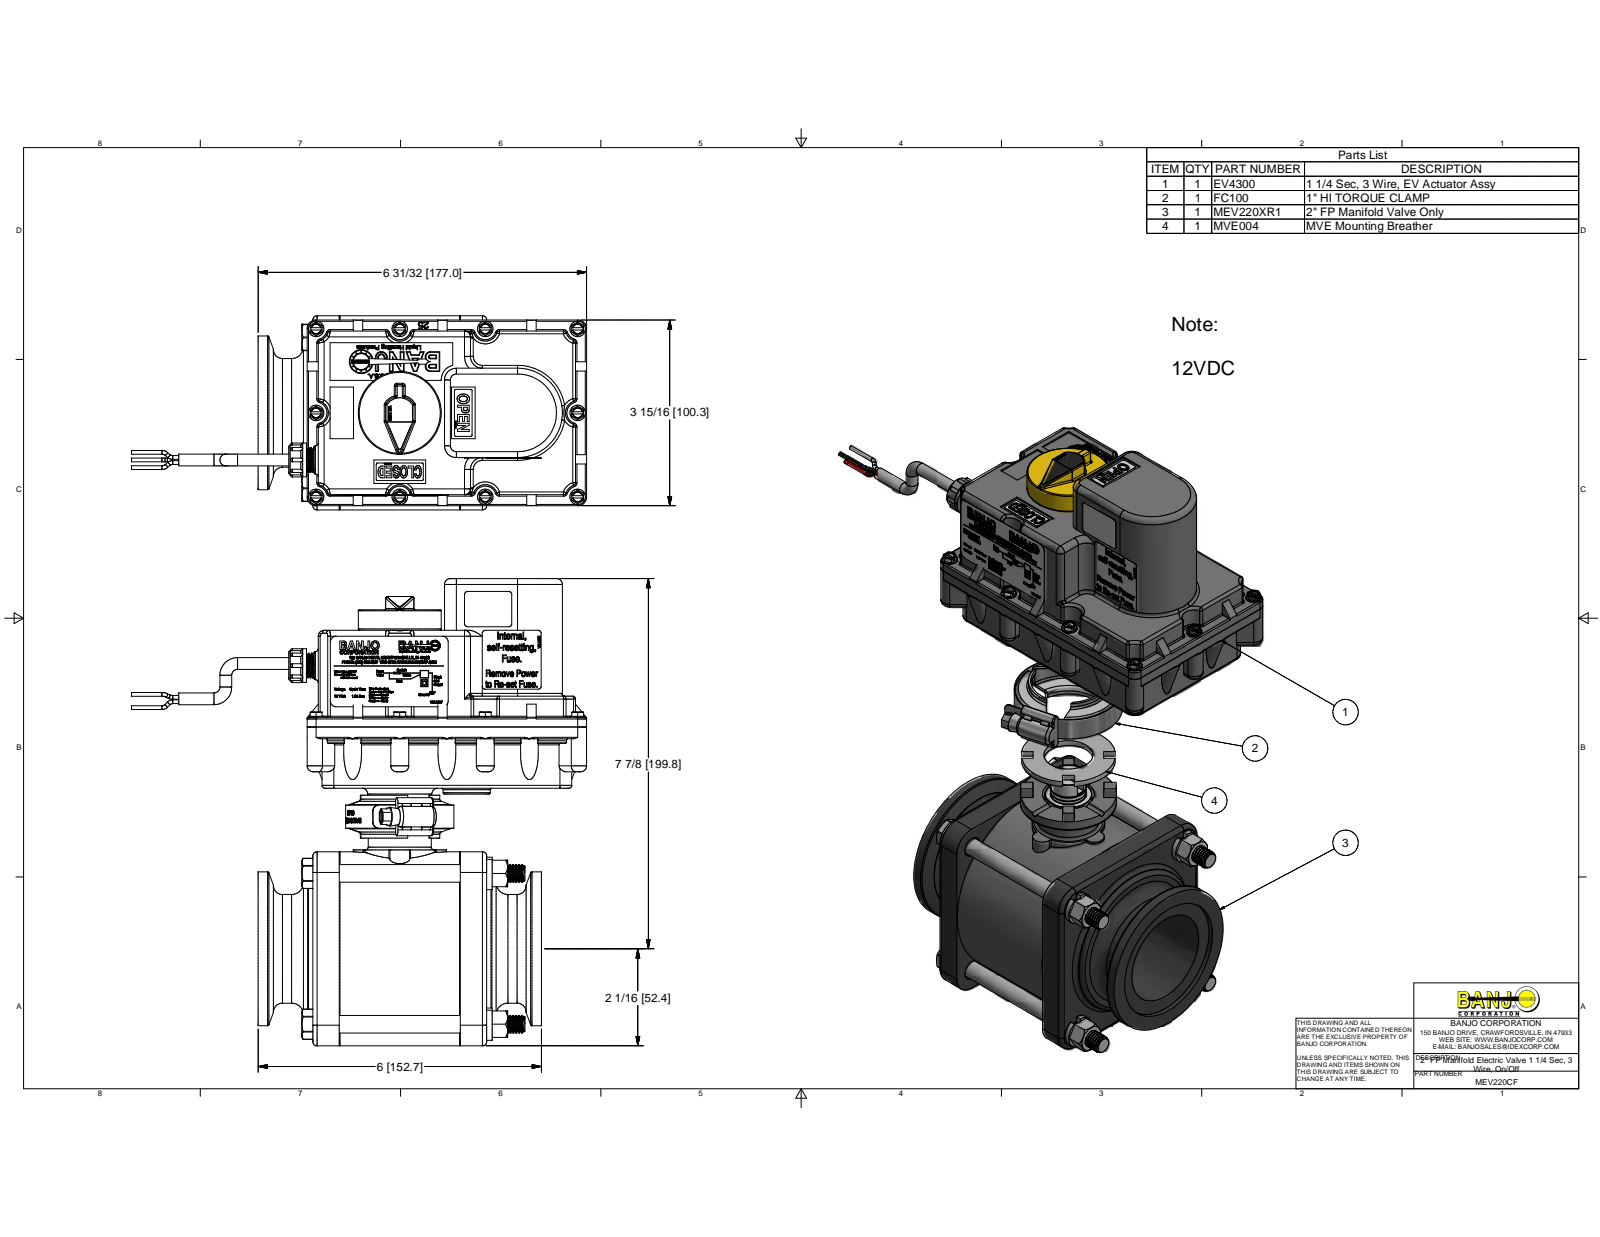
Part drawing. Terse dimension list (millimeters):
name: MEV25254AX; MEV25254A; VE25255SSH; MEV25151SS (+8 more)
written by: Autodesk Inventor 2016 (AUTOMOTIVE_DESIGN)
unit: mm
bodies: 78 solids, 11372 faces (5317 planar, 1561 cylindrical, 4494 other)
size: 252.22 × 245.26 × 104.78
volume: 1 330 000 mm³; area: 515 621 mm²
holes: 10× ⌀2.79, 10× ⌀4.06, 10× ⌀5.08, 8× ⌀1.52, 6× ⌀3.05, 6× ⌀3.81, 4× ⌀0.38, 4× ⌀2.26, 4× ⌀3.3, 4× ⌀3.45, 4× ⌀4.44, 4× ⌀4.47
bosses: 60× ⌀8.24, 10× ⌀8.33, 10× ⌀3.51, 9× ⌀6.35, 9× ⌀2.03, 8× ⌀2.62, 6× ⌀8, 6× ⌀7.62
rounds: 125× R0.76, 62× R0.51, 47× R1.52, 32× R3.17, 26× R1.59, 24× R8, 24× R12.7, 16× R9.91
face distances: 3.18, 5.08, 33.02, 20.07, 27.94, 1.9, 6.98, 3.17, 21.59, 65.15
hole spacings: 42.68, 52.27, 60.36, 45.34, 2.77, 8.84, 12.5, 30.18
